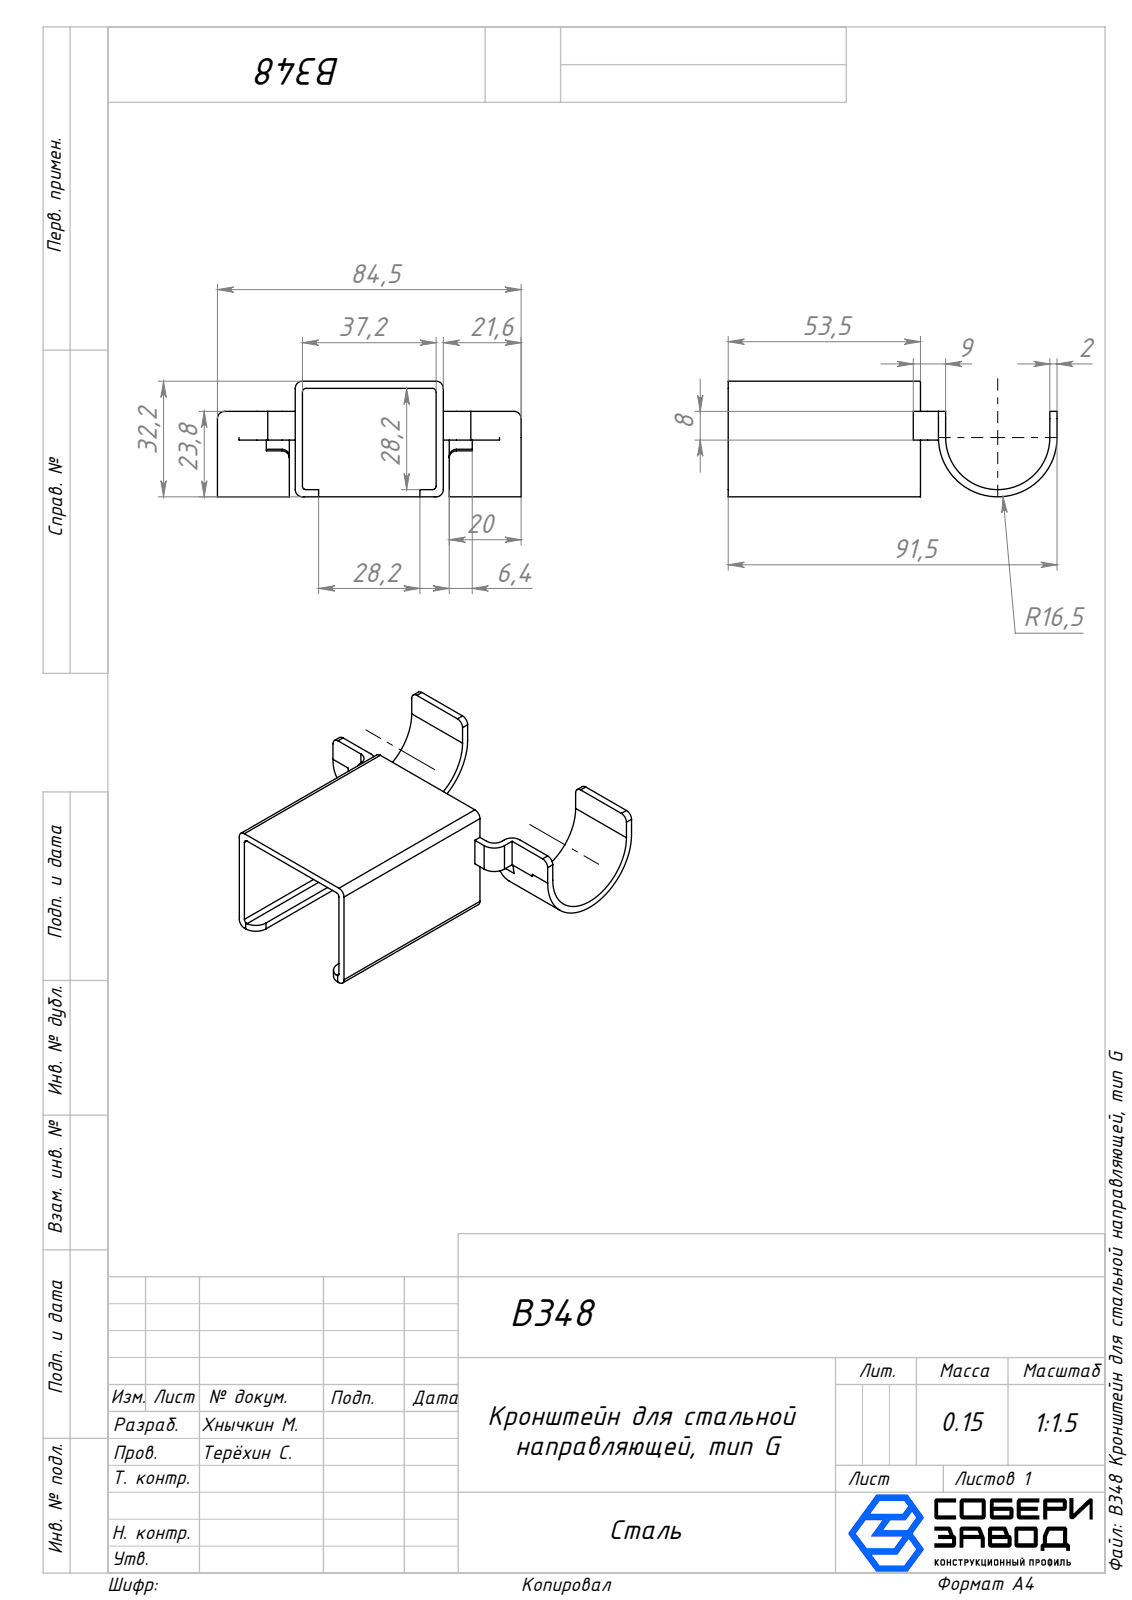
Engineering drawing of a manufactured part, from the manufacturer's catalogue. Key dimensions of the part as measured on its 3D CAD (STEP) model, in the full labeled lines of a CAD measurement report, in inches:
Part name (STEP PRODUCT): B348 Кронштейн для стальной направляющей, тип G
STEP written by: SolidWorks 2025 (AUTOMOTIVE_DESIGN)
Units: inches
Bodies: 1 solid, 76 faces (43 planar, 31 cylindrical, 2 other)
Overall size (bounding box): 3.602 × 3.327 × 1.268
Volume: 1.165 in³ · Surface area: 31.2 in²
Partial cylindrical surfaces — rounded edges, fillets, slot ends (radius × count): R0.079 ×10, R0.157 ×6, R0.118 ×5, R0.039 ×4, R0.571 ×1, R0.65 ×1
Main face-to-face distances: 0.079, 1.543, 1.622, 1.465, 1.189, 1.496, 1.268, 1.11, 0.276, 1.22
